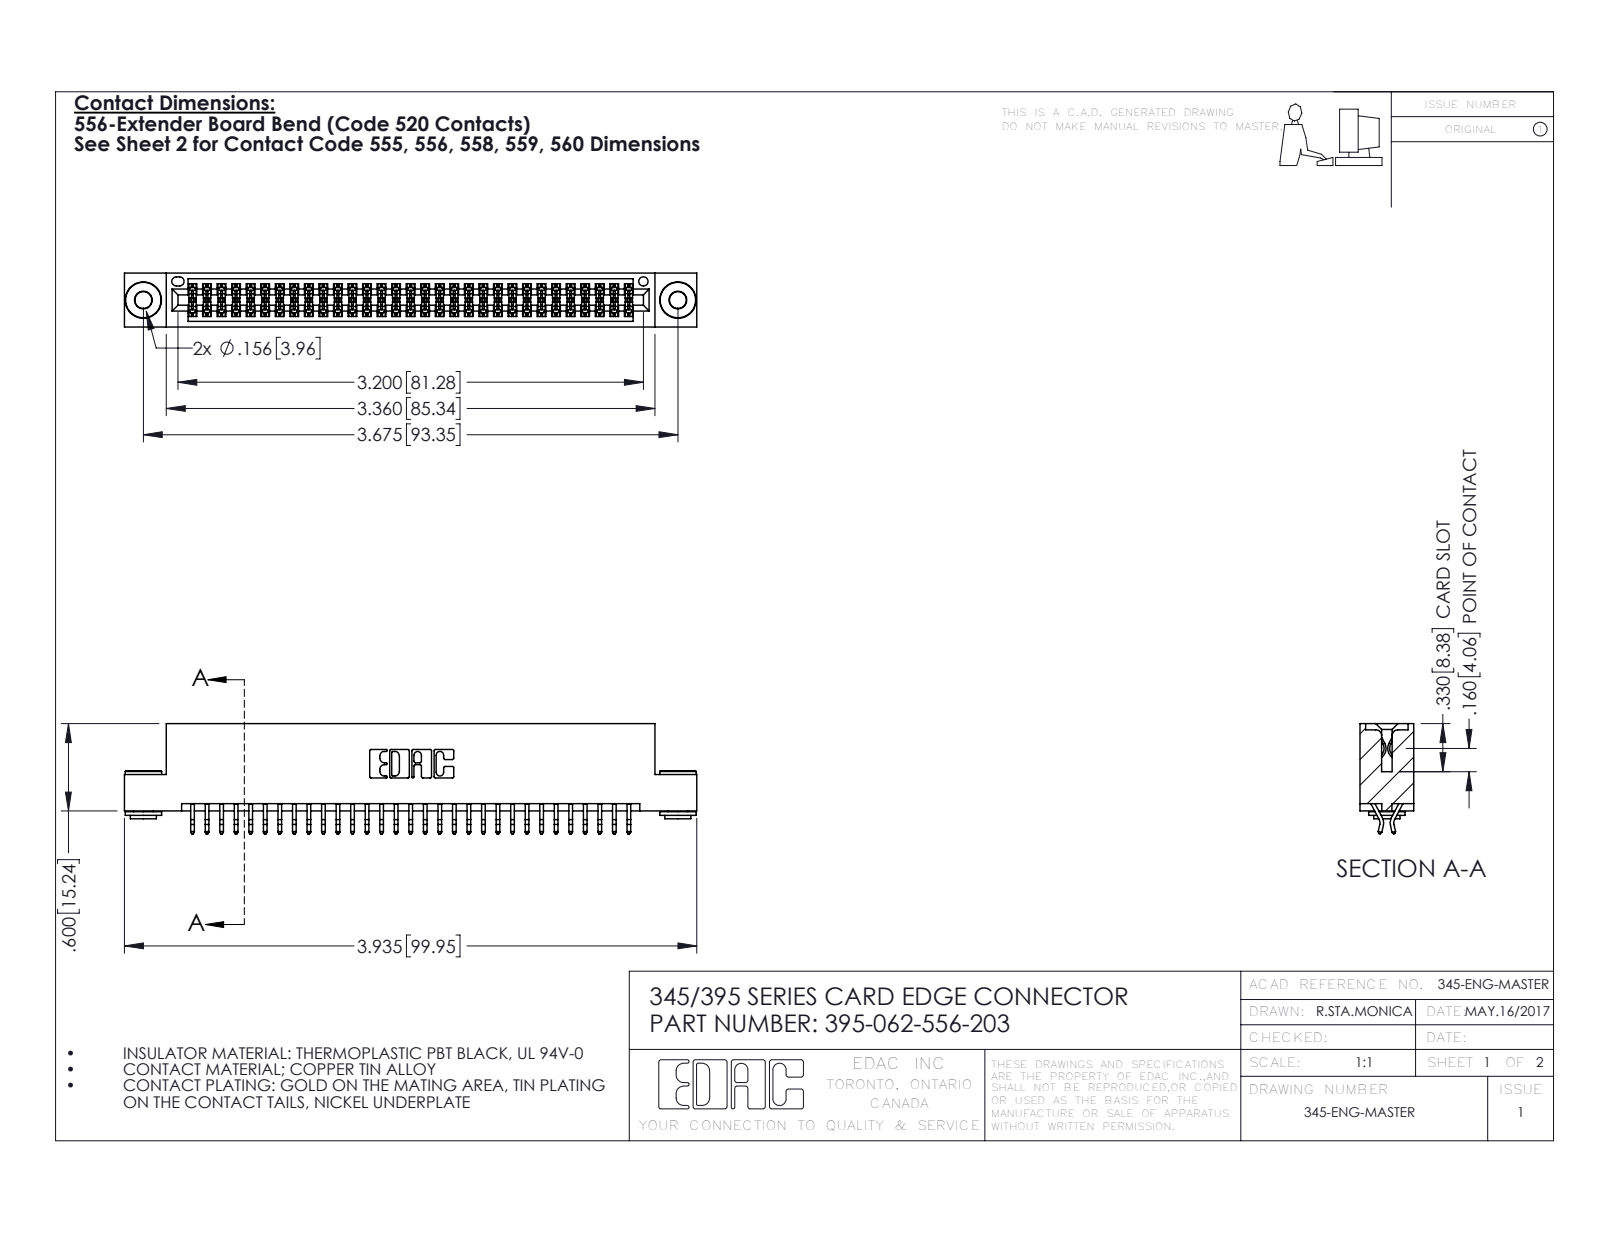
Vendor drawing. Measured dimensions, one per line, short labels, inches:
name: 395-062-556-203; 345-250-002_345-250-002-102; 345-292-001_556 Tail; 345 Part_Flush Mounting Lugs - 0.156 Dia-TH
written by: SolidWorks 2016 (CONFIG_CONTROL_DESIGN)
unit: in
bodies: 65 solids, 3636 faces (2384 planar, 1244 cylindrical, 8 other)
size: 3.935 × 0.757 × 0.37
volume: 0.587 in³; area: 21.95 in²
holes: 2× ⌀0.116, 2× ⌀0.156, 1× ⌀0.064
bosses: 2× ⌀0.25, 2× ⌀0.18, 2× ⌀0.136
rounds: 93× R0.006, 22× R0.01, 6× R0.007, 6× R0.031, 3× R0.026, 2× R0.01, 2× R0.014, 2× R0.019
face distances: 0.072, 0.298, 0.2, 0.37, 0.025, 0.098, 0.272, 0.225, 0.175, 0.149
hole spacings: 0.27, 3.44, 3.675
